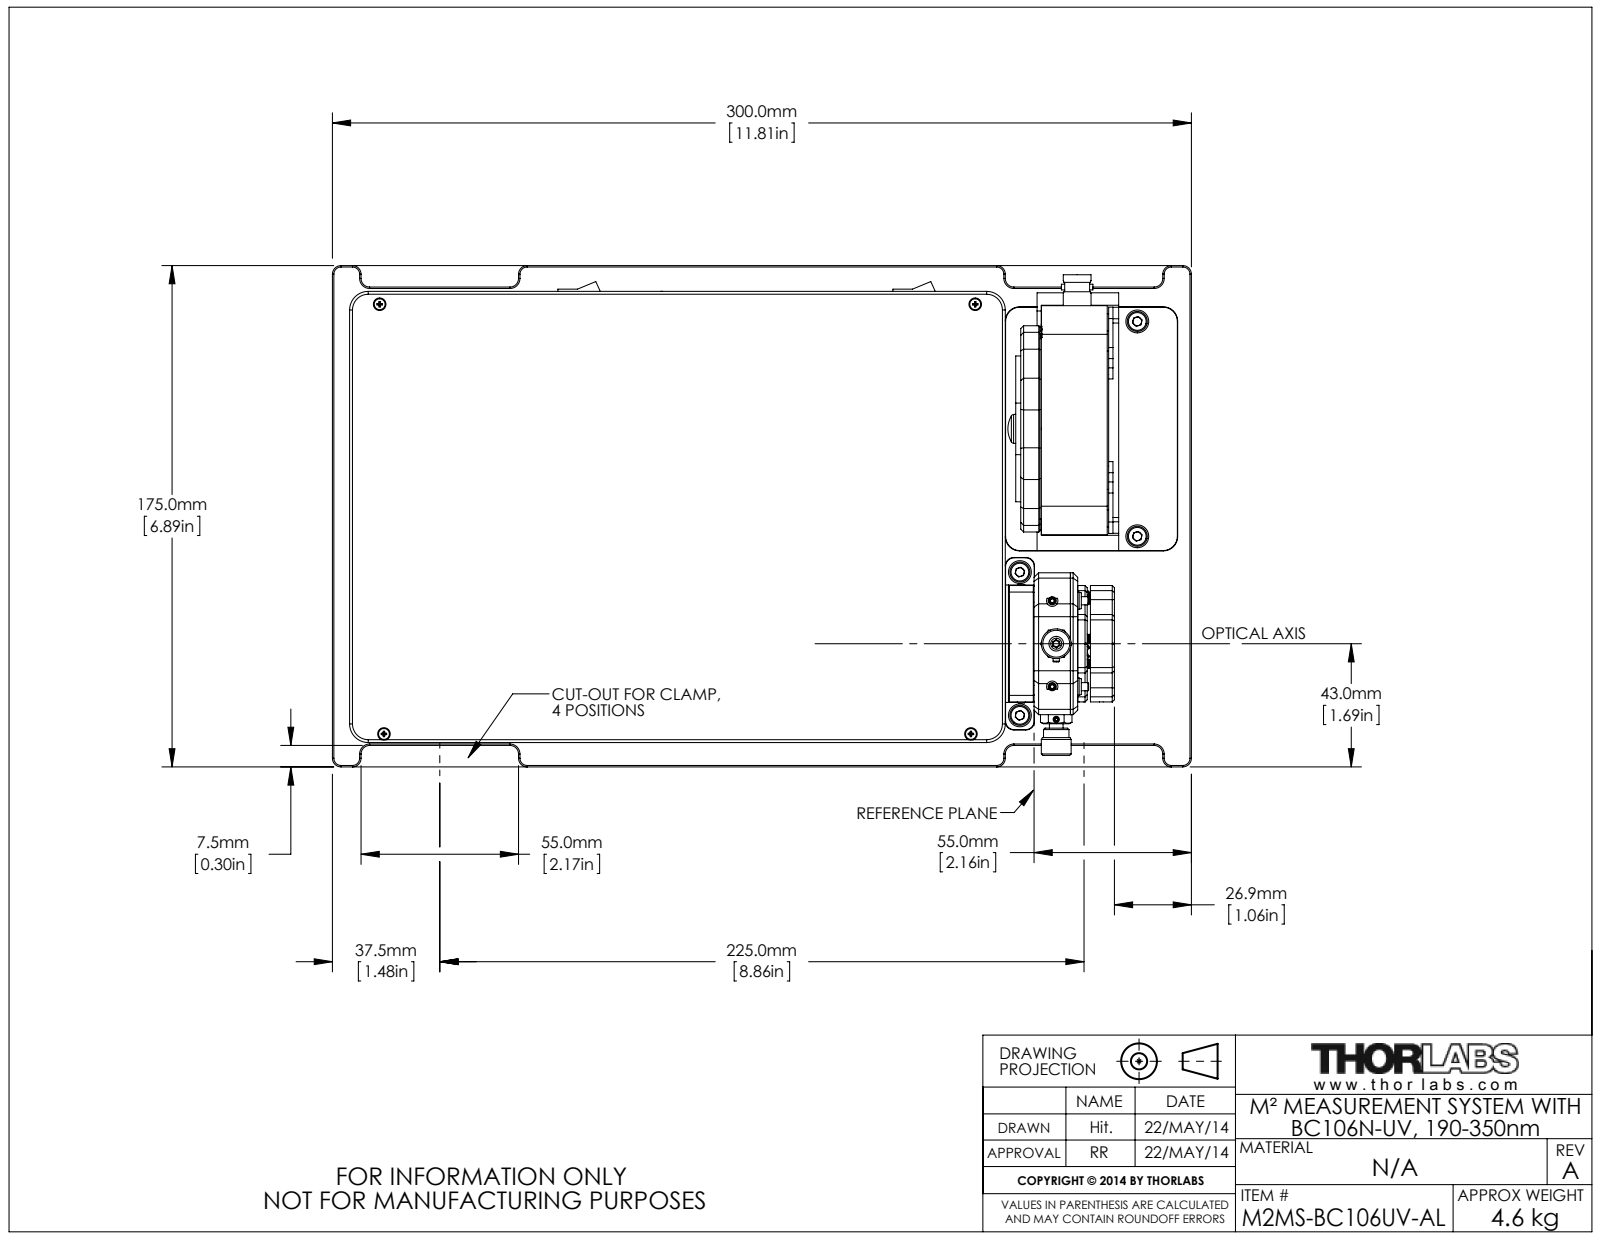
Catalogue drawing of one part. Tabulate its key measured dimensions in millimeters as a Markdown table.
| quantity | value |
| --- | --- |
| part name | Socket Head Cap Screw_DIN_DIN 912 M4 x 10 --- 10N; Countersunk Flat Head Cross Recess Screw_DIN_ISO 7046-1 - M2 x 6 - Z --- 6N; CXY1Q revised; M0093-1341-0d Abdeckung Teil2 M2 Set Redesign (+8 more) |
| STEP written by | SolidWorks 2013 (CONFIG_CONTROL_DESIGN) |
| units | millimeters |
| bodies | 134 solids, 22859 faces (13111 planar, 4931 cylindrical, 4817 other) |
| overall size | 300 × 175 × 126 |
| volume | 1 301 000 mm³ |
| surface area | 523 559 mm² |
| round holes (diameter × count) | 1.6 × 31, 0.91 × 30, 2.2 × 21, 0.81 × 16, 1.78 × 12, 3.3 × 12, 4 × 11, 0.6 × 10, 1.85 × 10, 5 × 10, 2.26 × 8, 2.3 × 8 |
| round bosses / shafts (diameter × count) | 1 × 15, 2 × 14, 1.1 × 14, 4 × 10, 3 × 10, 3.8 × 8, 3.18 × 8, 1.59 × 8 |
| partial cylindrical surfaces (radius × count) | 0.15 × 193, 0.2 × 76, 3 × 72, 0.1 × 69, 0.5 × 57, 0.3 × 51, 1 × 46, 4 × 28 |
| main face-to-face distances | 3, 90.7, 1.5, 87.7, 21.2, 66.5, 69.5, 75.5, 6, 15.2 |
| hole center spacings | 16.12, 30, 39.81, 0.94, 5.89, 8.93, 17.64, 17.88 |
